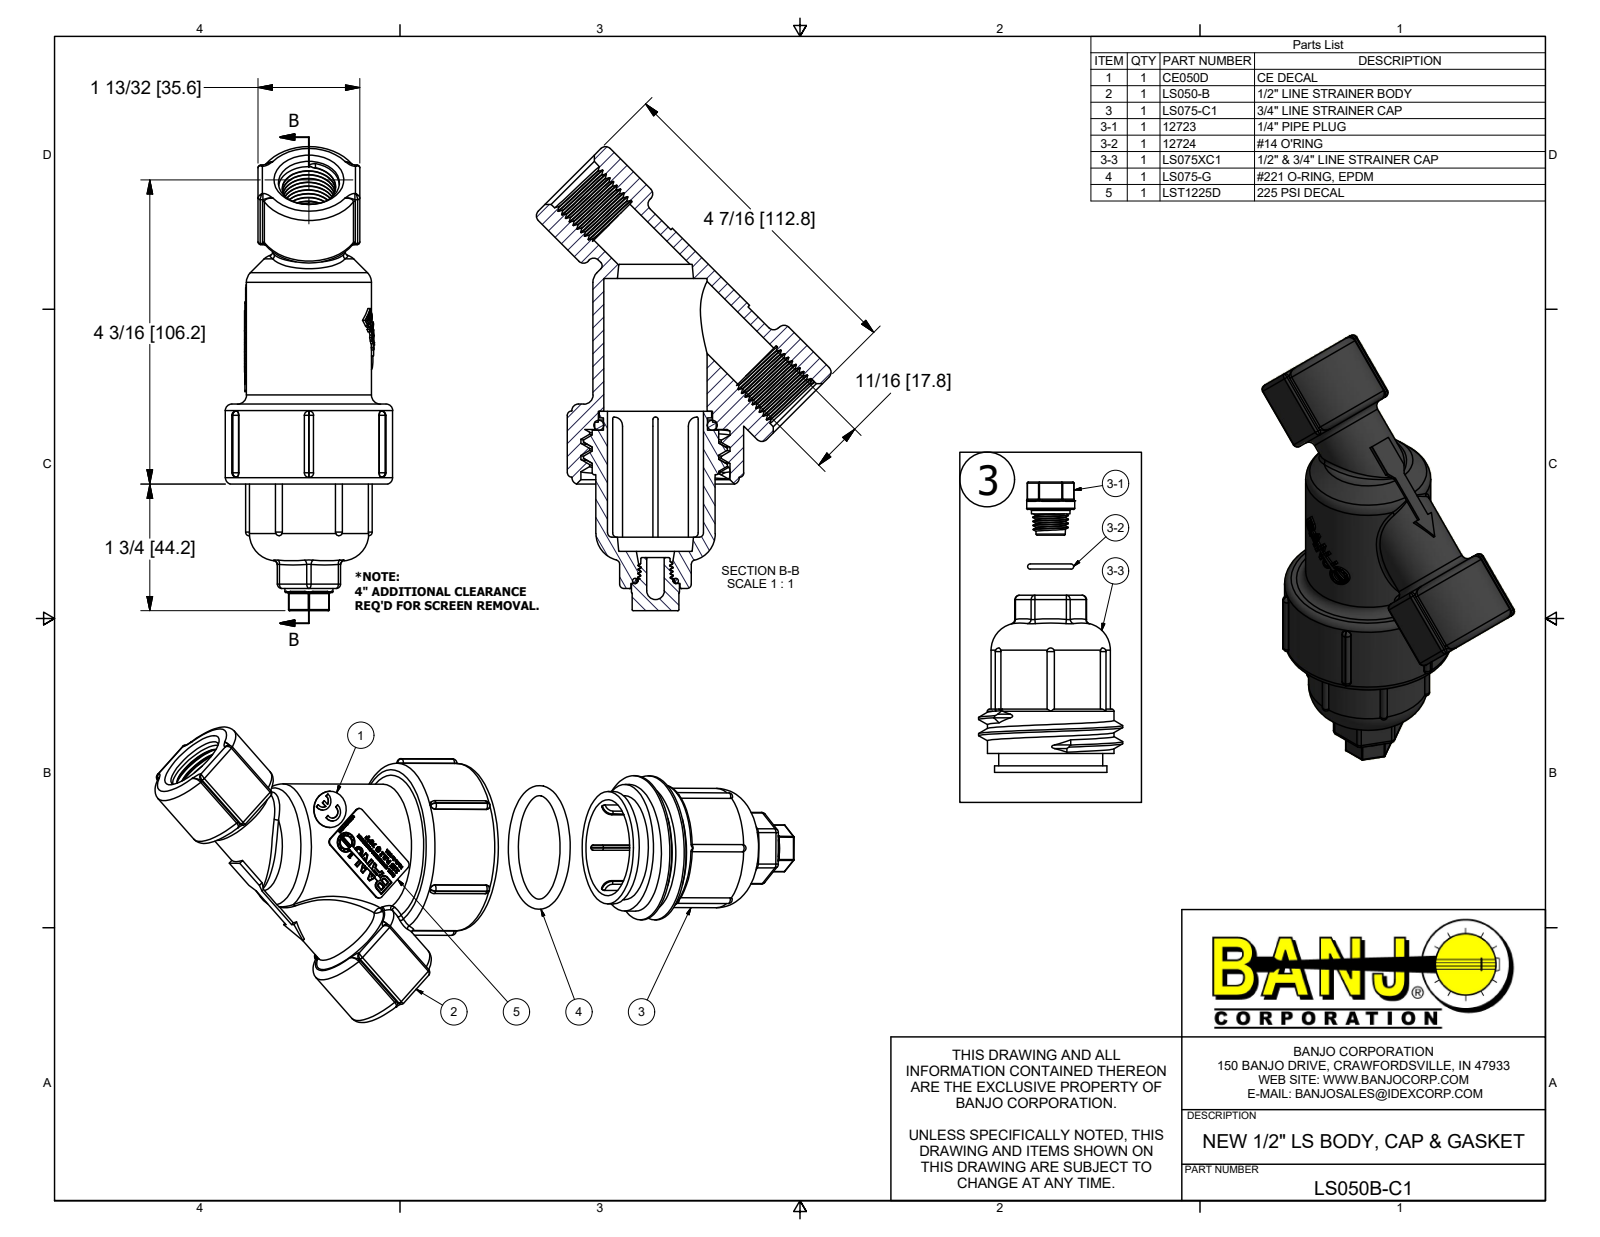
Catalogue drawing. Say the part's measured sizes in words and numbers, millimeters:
The part is named "LS050B-C1; CE050D; LS050-B; LS075-C1 (+5 more)". Its 3-D file was written by "Autodesk Inventor 2018 (AUTOMOTIVE_DESIGN)". It is 7 solids with 1983 faces: 1020 planar, 312 cylindrical and 651 other. Overall it measures 407.9 by 407.9 by 58.4 millimeters. Its volume is 210 400 cubic millimeters and its surface area 95 100 square millimeters. Round holes: 2 of diameter 4.6, 2 of diameter 6.5, 2 of diameter 17.8, 1 of diameter 6.1, 1 of diameter 17.1, 1 of diameter 33.5, 1 of diameter 36.1, 1 of diameter 39.9, 1 of diameter 42.4, 1 of diameter 45.9, 1 of diameter 52.1. Round bosses or shafts: 2 of diameter 6.9, 1 of diameter 58.4, 1 of diameter 50.3, 1 of diameter 44.2, 1 of diameter 43.7, 1 of diameter 41.7, 1 of diameter 39.2, 1 of diameter 36.3. Partial cylindrical surfaces (rounded edges, fillets, slot ends): 75 of radius 1.5, 34 of radius 0.8, 18 of radius 0.4, 8 of radius 3.2, 6 of radius 1.3, 4 of radius 0.7, 4 of radius 0.8, 4 of radius 1.6. The main face-to-face distances are 4.1, 6.4, 35.6, 39.6, 1.8, 40.1, 6.6, 0.5, 53, 52.7. The hole center spacings are 16.2.
